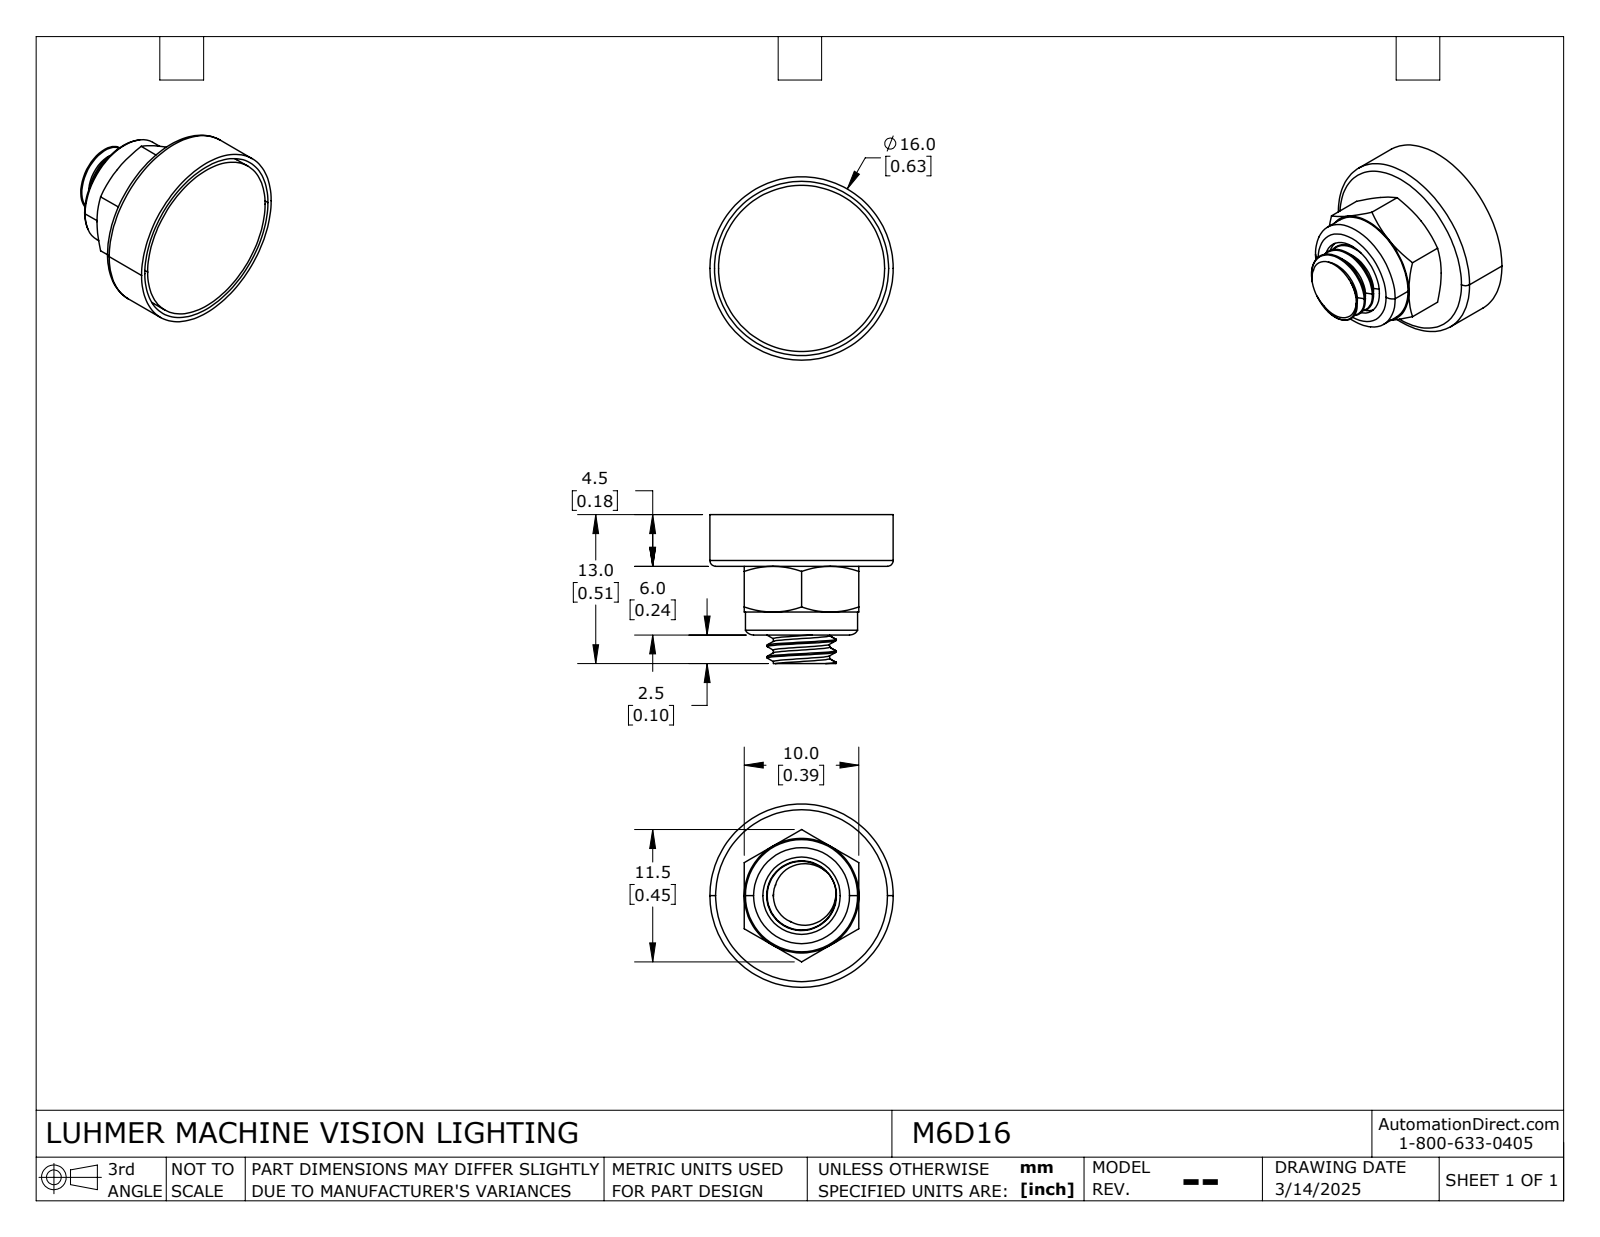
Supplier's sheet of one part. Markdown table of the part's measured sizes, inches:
| quantity | value |
| --- | --- |
| part name | M6D16 |
| STEP written by | SolidWorks 2024 (AUTOMOTIVE_DESIGN) |
| units | inches |
| bodies | 2 solids, 92 faces (17 planar, 16 cylindrical, 59 other) |
| overall size | 0.63 × 0.63 × 0.512 |
| volume | 0.085 in³ |
| surface area | 2.446 in² |
| round holes (diameter × count) | 0.194 × 1, 0.266 × 1, 0.598 × 1 |
| round bosses / shafts (diameter × count) | 0.63 × 1, 0.571 × 1, 0.386 × 1 |
| main face-to-face distances | 0.177, 0.394, 0.059, 0.236, 0.335, 0.118, 0.217, 0.02, 0.157, 0.512 |
